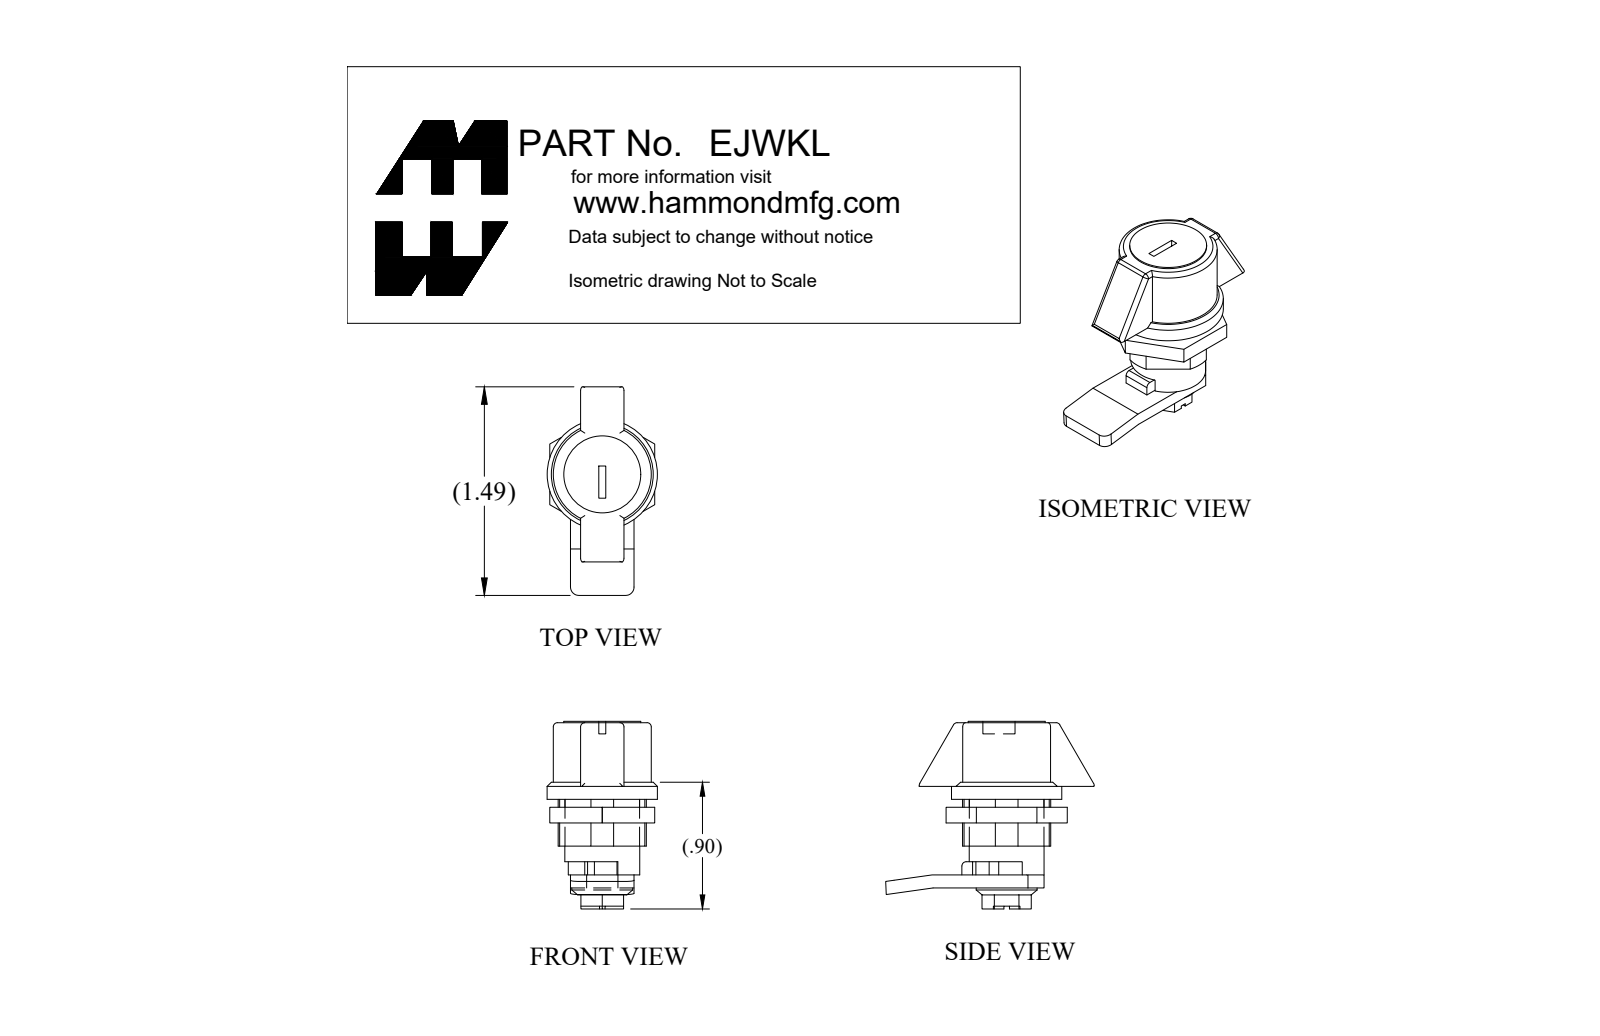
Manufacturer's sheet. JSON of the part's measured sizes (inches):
{"part_name": "EJWKL_Default", "step_written_by": "SolidWorks 2019 (CONFIG_CONTROL_DESIGN)", "units": "inches", "bodies": {"solids": 1, "faces": 133, "planar": 84, "cylindrical": 37, "other": 12}, "overall_size": [1.489, 1.34, 0.788], "volume_in3": 0.486, "surface_area_in2": 5.409, "round_bosses_or_shafts": [[0.788, 1], [0.55, 1], [0.535, 1], [0.435, 1]], "partial_cylinders_radius": [[0.03, 11], [0.06, 2], [0.125, 1], [0.315, 1], [0.35, 1]], "face_to_face_distances": [0.093, 0.726, 0.614, 0.557, 0.169, 0.112, 0.057, 0.371, 0.483, 0.54]}
